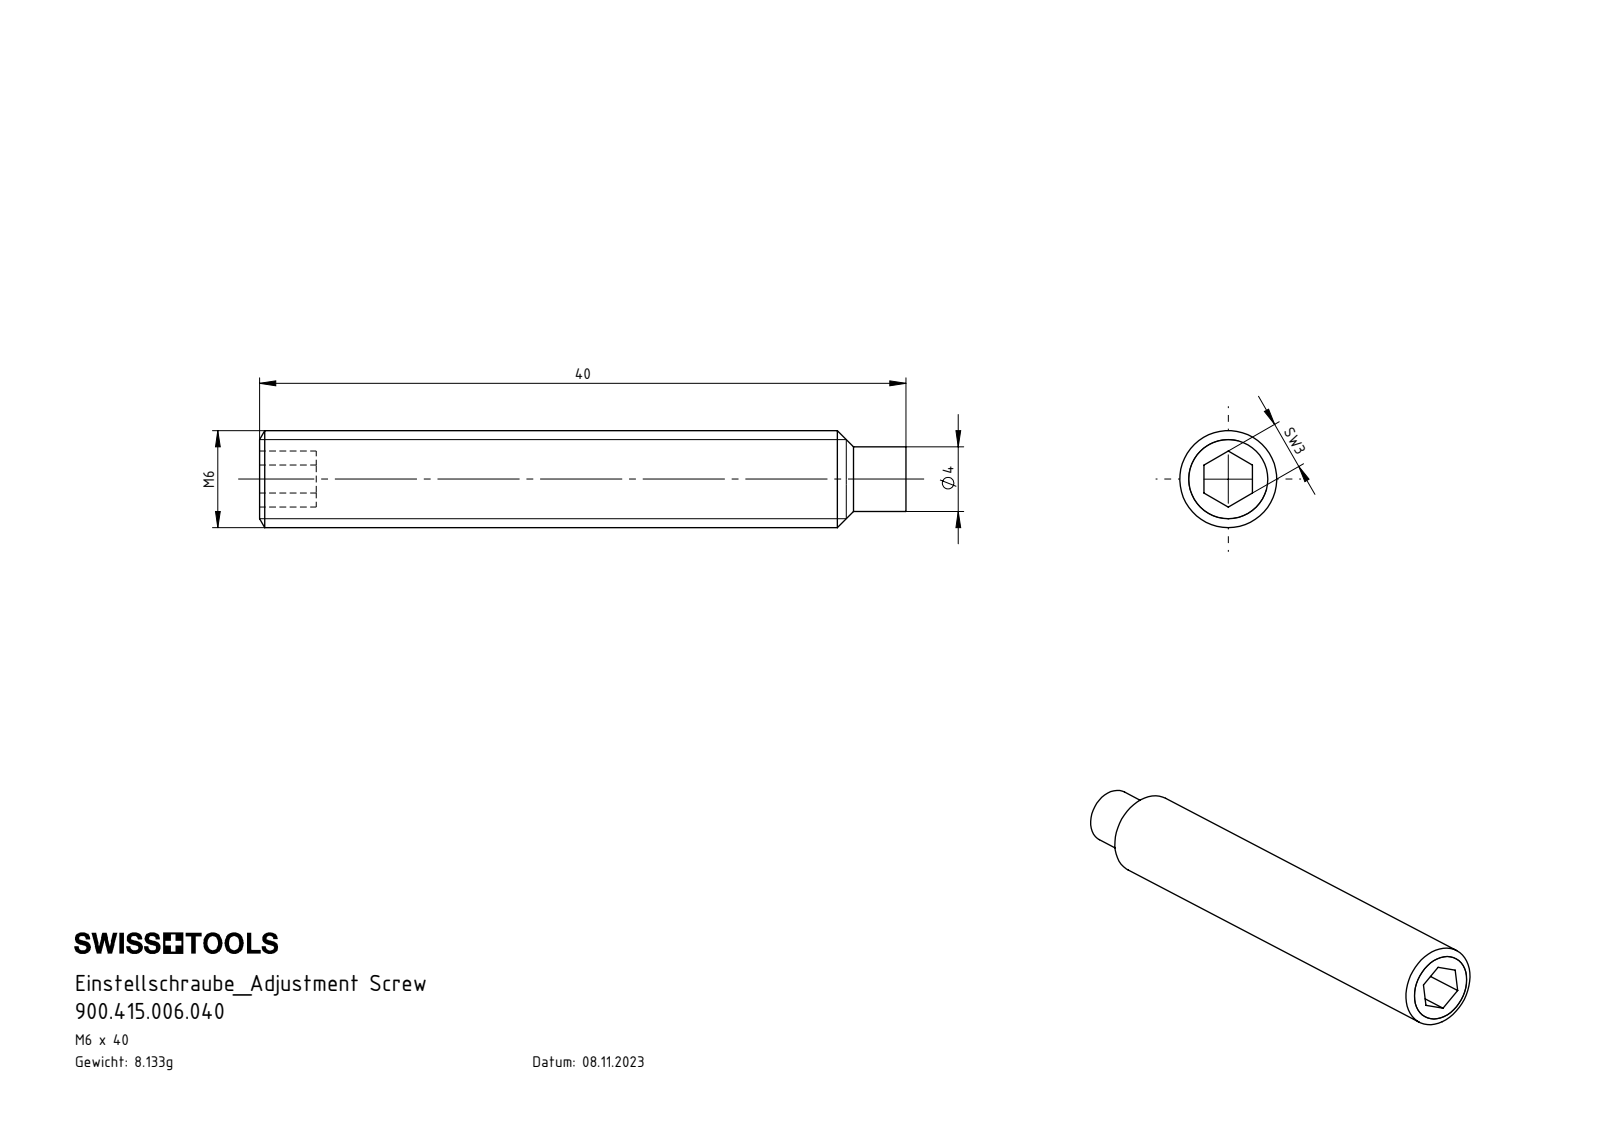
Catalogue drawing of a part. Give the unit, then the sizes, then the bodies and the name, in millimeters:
Units: millimetres
Overall size (bounding box): 40 × 6 × 6
Round bosses / shafts (diameter × count): ⌀6 ×1, ⌀4 ×1
Main face-to-face distances: 3, 40, 3.5, 36.5
Volume: 1 043 mm³ · Surface area: 810 mm²
Bodies: 1 solid, 17 faces (9 planar, 4 cylindrical, 4 other)
Part name (STEP PRODUCT): 900.415.006.040
STEP written by: SolidWorks 2022 (AUTOMOTIVE_DESIGN)
